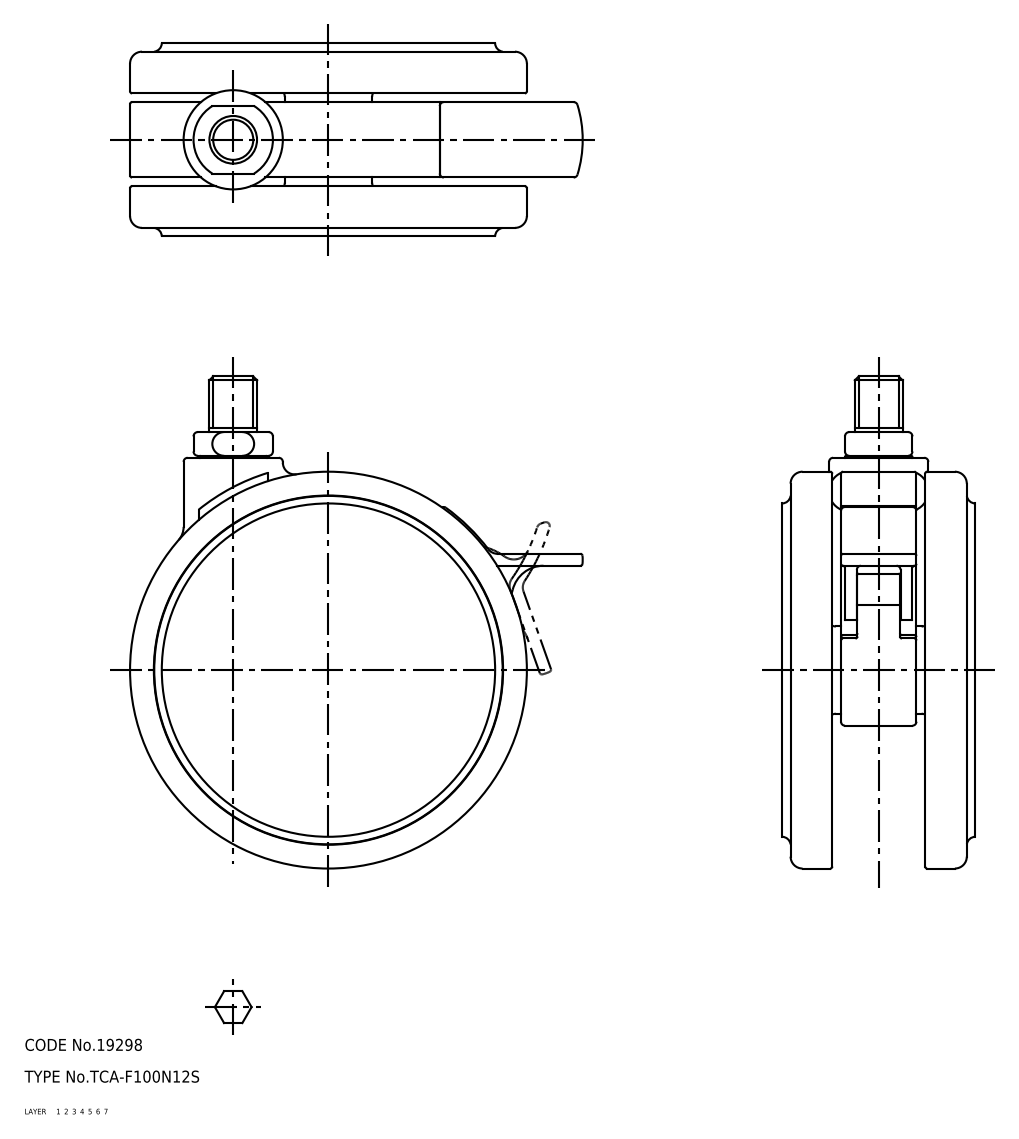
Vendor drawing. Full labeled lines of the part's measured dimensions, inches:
Part name (STEP PRODUCT): TCA-F100N12S; caster
STEP written by: SolidWorks 2015 (AUTOMOTIVE_DESIGN)
Units: inches
Bodies: 1 solid, 1520 faces (528 planar, 654 cylindrical, 338 other)
Overall size (bounding box): 4.882 × 4.491 × 1.913
Volume: 11.32 in³ · Surface area: 148.3 in²
Round holes (diameter × count): ⌀0.094 ×1, ⌀0.118 ×1, ⌀0.13 ×1, ⌀0.142 ×1, ⌀0.228 ×1, ⌀0.24 ×1, ⌀0.318 ×1, ⌀0.354 ×1, ⌀0.366 ×1, ⌀0.421 ×1, ⌀0.484 ×1, ⌀0.512 ×1
Round bosses / shafts (diameter × count): ⌀3.937 ×1, ⌀3.457 ×1, ⌀0.984 ×1, ⌀0.866 ×1, ⌀0.787 ×1, ⌀0.669 ×1, ⌀0.472 ×1, ⌀0.413 ×1
Partial cylindrical surfaces — rounded edges, fillets, slot ends (radius × count): R0.02 ×63, R0.039 ×61, R0.059 ×21, R0.008 ×18, R0.012 ×17, R0.079 ×16, R0.118 ×7, R0.028 ×2
Main face-to-face distances: 0.071, 1.772, 1.843, 0.142, 1.701, 0.496, 1.276, 0.354, 1.417, 0.425
Hole centre spacings: 0.843, 1.18, 1.732
